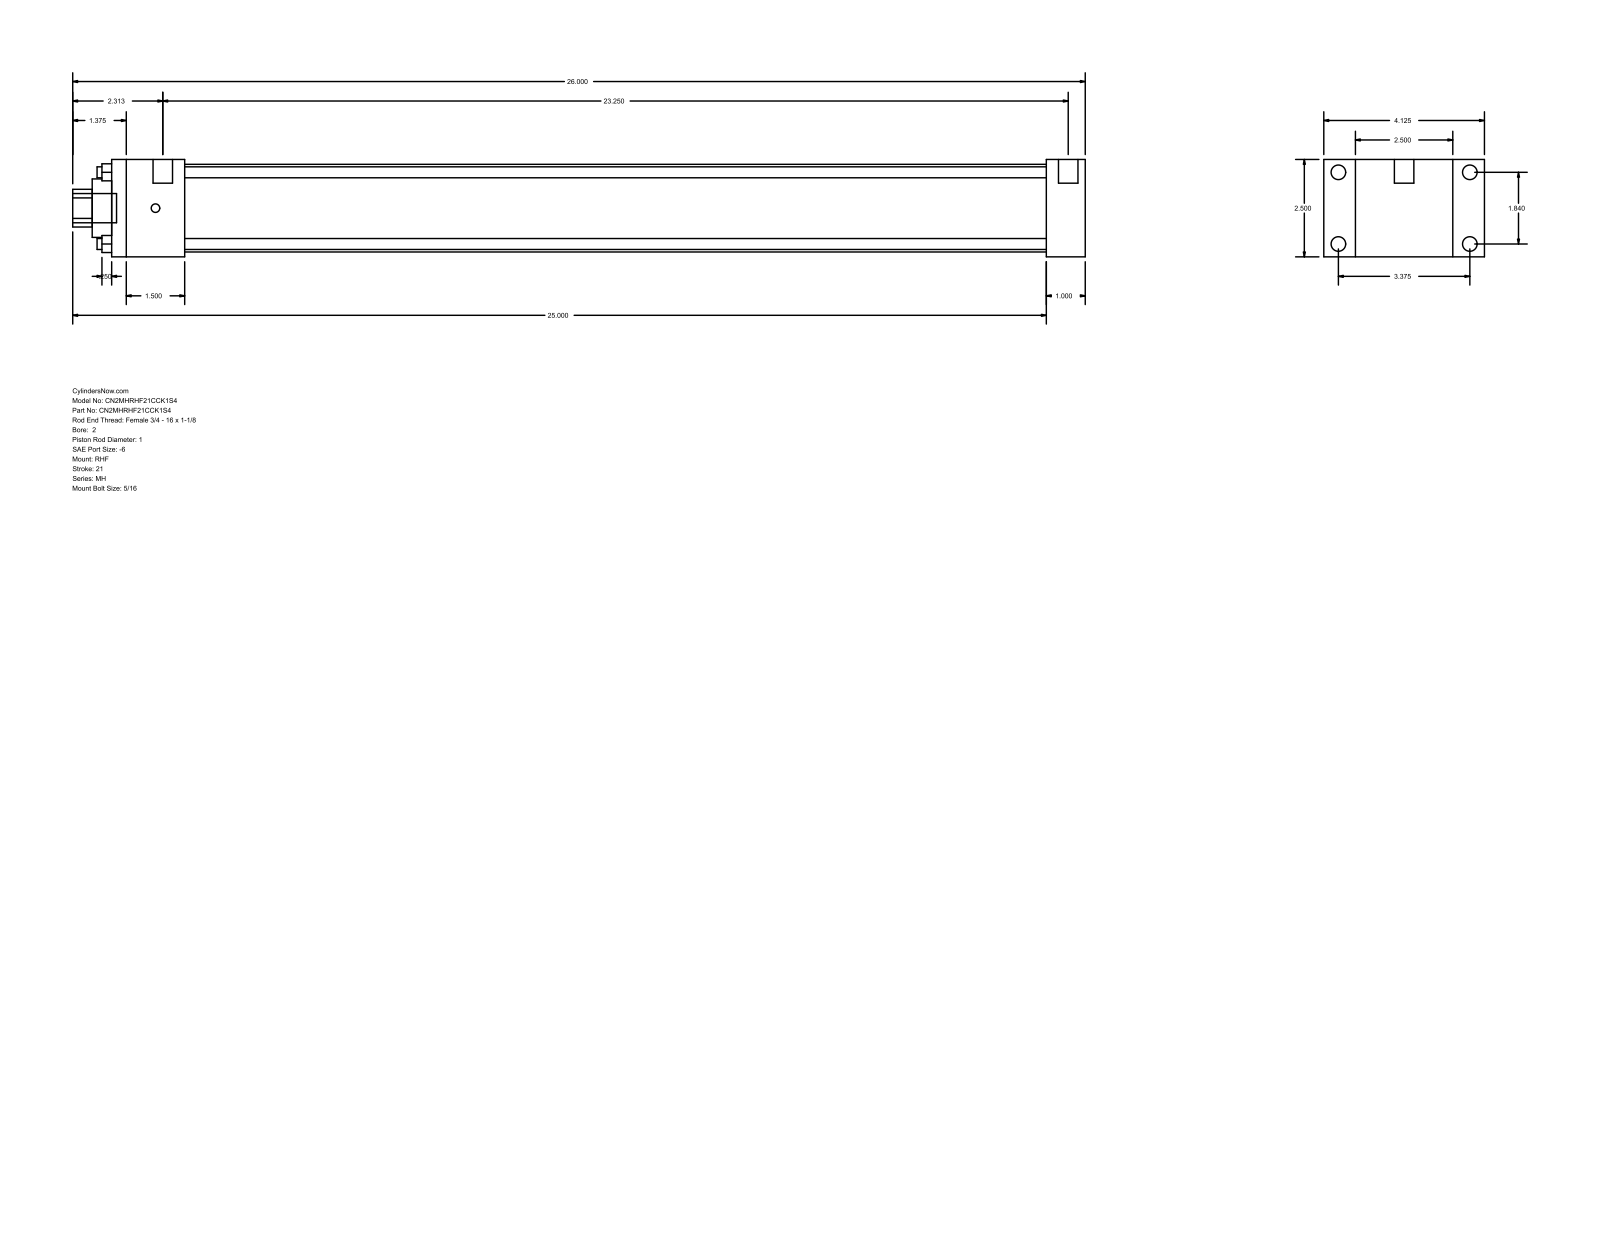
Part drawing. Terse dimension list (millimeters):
name: MH_RHF__0200_1
written by: GSSL Pune (CONFIG_CONTROL_DESIGN)
unit: mm
bodies: 0 solids, 88 faces (60 planar, 28 cylindrical, 0 other)
size: 660.4 × 104.78 × 63.5
holes: 4× ⌀7.14, 1× ⌀25.4, 1× ⌀38.1, 1× ⌀57.15
bosses: 4× ⌀9.53, 4× ⌀5.56, 2× ⌀12.7, 1× ⌀19.05
rounds: 1× R12.29
face distances: 63.5, 25.4, 20.64, 84.14, 635, 609.6, 104.78, 47.63, 561.97, 587.37
hole spacings: 33.05, 46.74, 66.1
